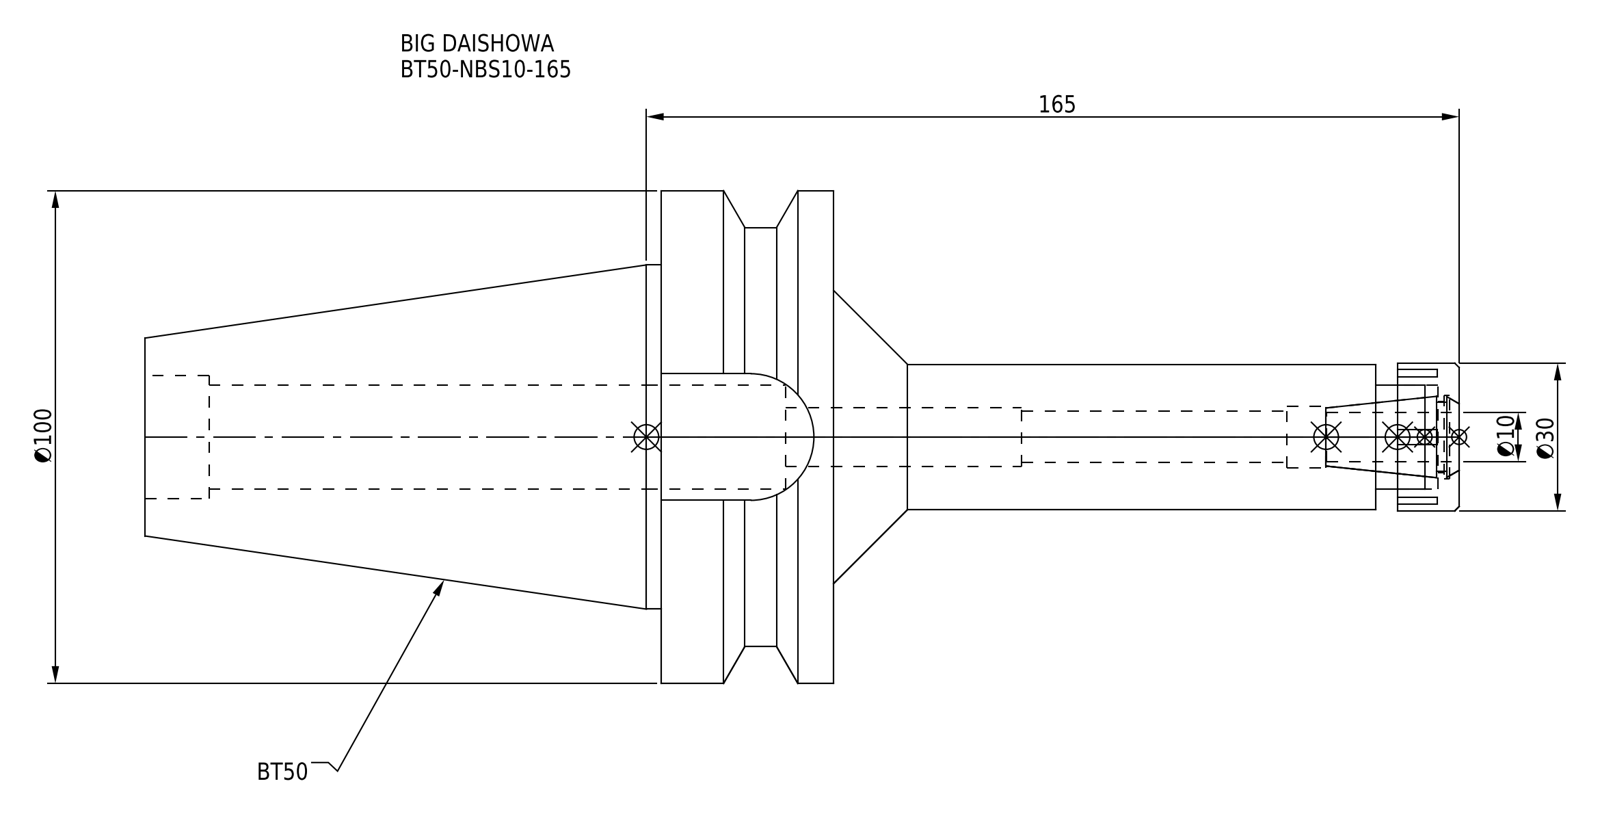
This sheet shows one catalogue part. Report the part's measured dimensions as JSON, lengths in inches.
{"part_name": "BT50-NBS10-165; DXF_TEMP_ASSY_ASM_4_ASM.stp; BT50NB10165-100_ASM.stp; BT50-NBS10-165-FreeParts (+3 more)", "step_written_by": "SolidWorks 2019 (CONFIG_CONTROL_DESIGN)", "units": "inches", "bodies": {"solids": 2, "faces": 93, "planar": 45, "cylindrical": 34, "other": 14}, "overall_size": [10.504, 3.937, 3.937], "volume_in3": 32.33, "surface_area_in2": 111.7, "round_holes": [[0.409, 1], [0.472, 1], [0.492, 1], [0.571, 1], [0.669, 1], [0.827, 1], [0.835, 1], [0.984, 1]], "round_bosses_or_shafts": [[3.937, 1], [3.346, 1], [2.75, 1], [1.181, 1], [1.161, 1]], "partial_cylinders_radius": [[0.506, 1]], "face_to_face_distances": [1.378, 5.504, 4.126, 2.787, 5, 6.378, 10.504, 1.012, 0.177, 0.492]}
